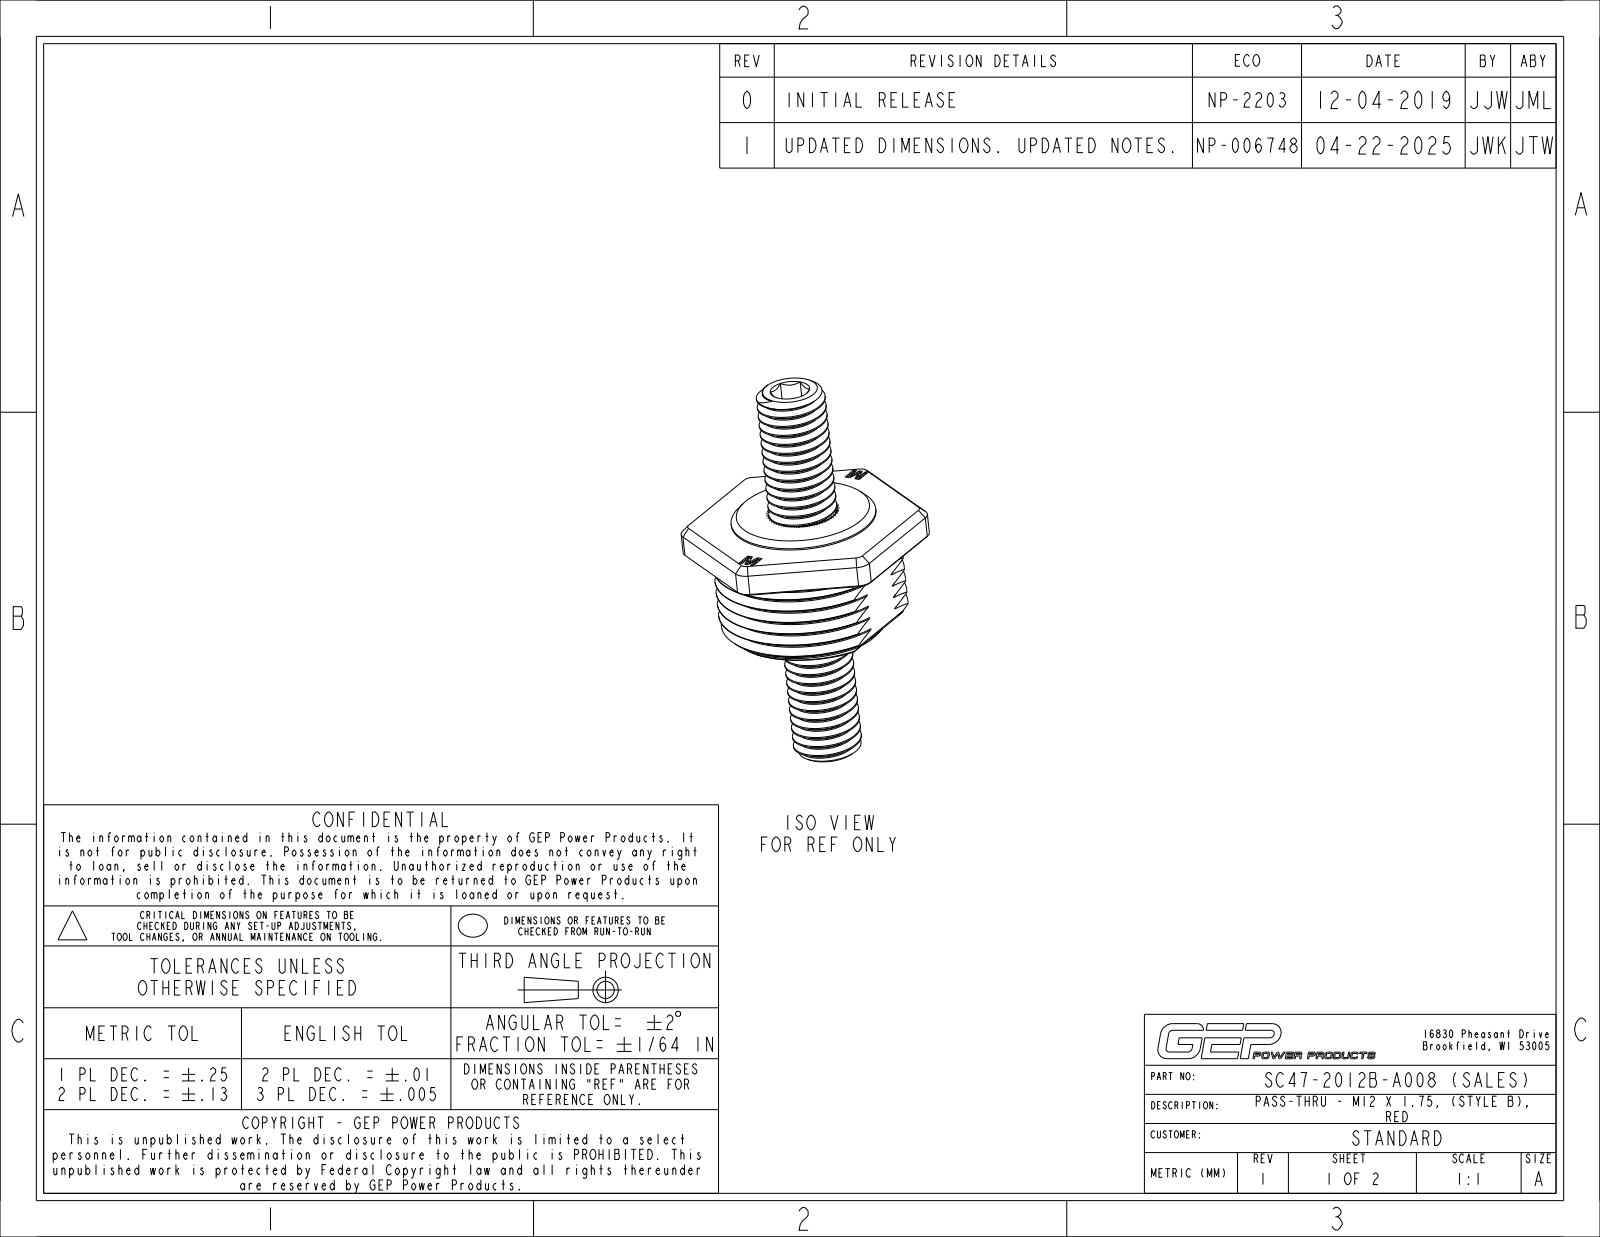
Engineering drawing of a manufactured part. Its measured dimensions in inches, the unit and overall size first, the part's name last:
Units: inches
Overall size (bounding box): 2.756 × 1.701 × 1.5
Round holes (diameter × count): ⌀0.402 ×1, ⌀0.84 ×1, ⌀1 ×1
Round bosses / shafts (diameter × count): ⌀0.472 ×1
Partial cylindrical surfaces — rounded edges, fillets, slot ends (radius × count): R0.005 ×16, R0.1 ×6, R0.03 ×2, R0.652 ×1
Main face-to-face distances: 0.574, 0.05, 0.573, 0.85, 0.25, 0.2, 0.65, 0.9, 0.6, 1.5
Volume: 1.388 in³ · Surface area: 24.08 in²
Bodies: 4 solids, 676 faces (323 planar, 190 cylindrical, 163 other)
Part name (STEP PRODUCT): C40-1001-X_MOLD_NCF; PC07-2000A-C000_NCF; PC40-2000A-B00X_NCF_ASM; PC05-2005A-A000_NCF (+2 more)
STEP written by: CREO PARAMETRIC BY PTC INC, 2024014 (CONFIG_CONTROL_DESIGN)
